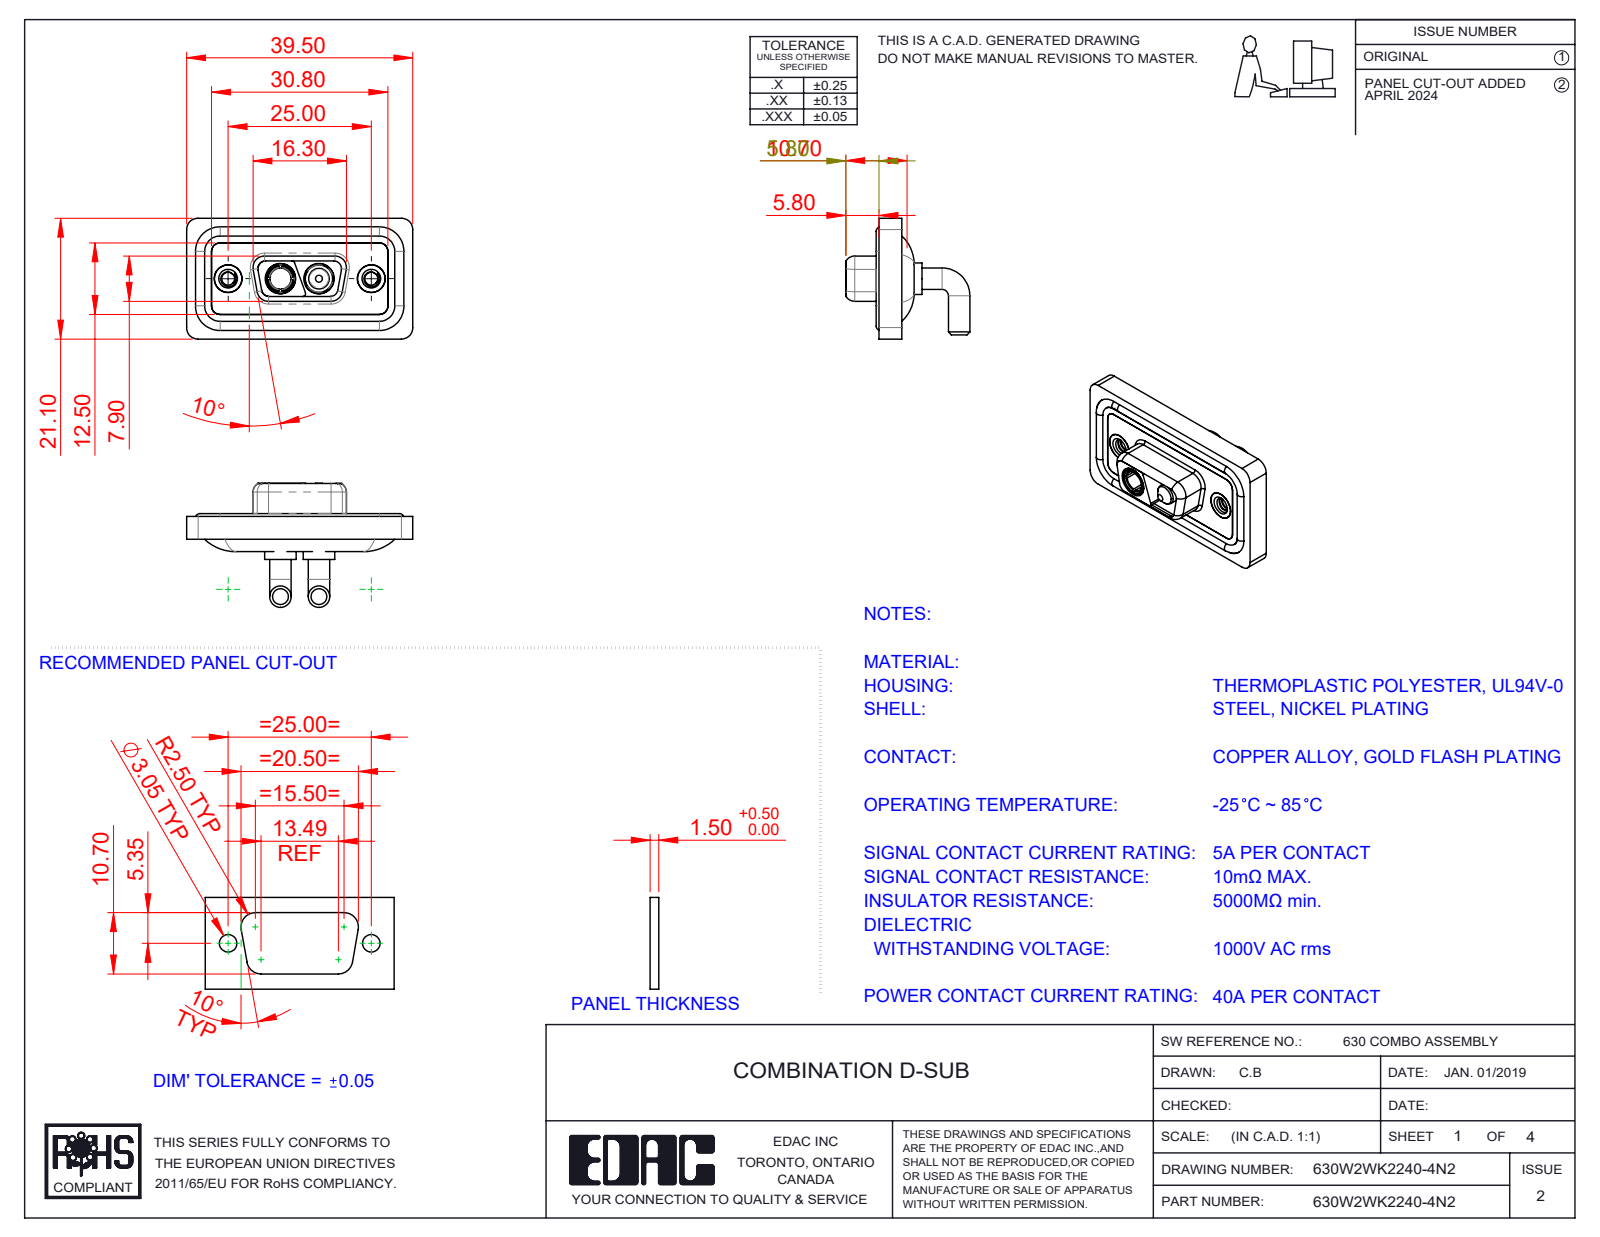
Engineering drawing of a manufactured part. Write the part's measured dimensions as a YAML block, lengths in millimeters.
part_name: "Power Socket_40A RA; 630Combo Housing_2WK2; 630Combo Shell Front_09 Contacts; 630Combo Threaded Rivet_2 (+4 more)"
step_written_by: "SolidWorks 2023 (CONFIG_CONTROL_DESIGN)"
units: millimeters
bodies: {solids: 11, faces: 508, planar: 144, cylindrical: 235, other: 129}
overall_size: [39.5, 21.68, 21.1]
volume: 4852
surface_area: 7582
round_holes:
  - {diameter: 4.85, count: 4}
  - {diameter: 2.26, count: 2}
  - {diameter: 4, count: 2}
  - {diameter: 4.05, count: 2}
  - {diameter: 5, count: 2}
  - {diameter: 5.3, count: 2}
  - {diameter: 3.7, count: 1}
round_bosses_or_shafts:
  - {diameter: 3.75, count: 4}
  - {diameter: 1.6, count: 4}
  - {diameter: 5.5, count: 2}
  - {diameter: 5.2, count: 2}
  - {diameter: 4.95, count: 2}
  - {diameter: 4.8, count: 2}
  - {diameter: 4.75, count: 2}
  - {diameter: 4.96, count: 1}
partial_cylinders:
  - {radius: 1.5, count: 18}
  - {radius: 2, count: 18}
  - {radius: 1.35, count: 8}
  - {radius: 1.6, count: 8}
  - {radius: 0.5, count: 6}
  - {radius: 0.25, count: 4}
  - {radius: 0.6, count: 4}
  - {radius: 0.65, count: 4}
face_to_face_distances: [0.4, 1.1, 2.9, 1.8, 2.5, 1.6, 3.1, 2.1, 3.7, 1.5]
hole_center_spacings: [9.14, 15.86, 6.72, 25]
